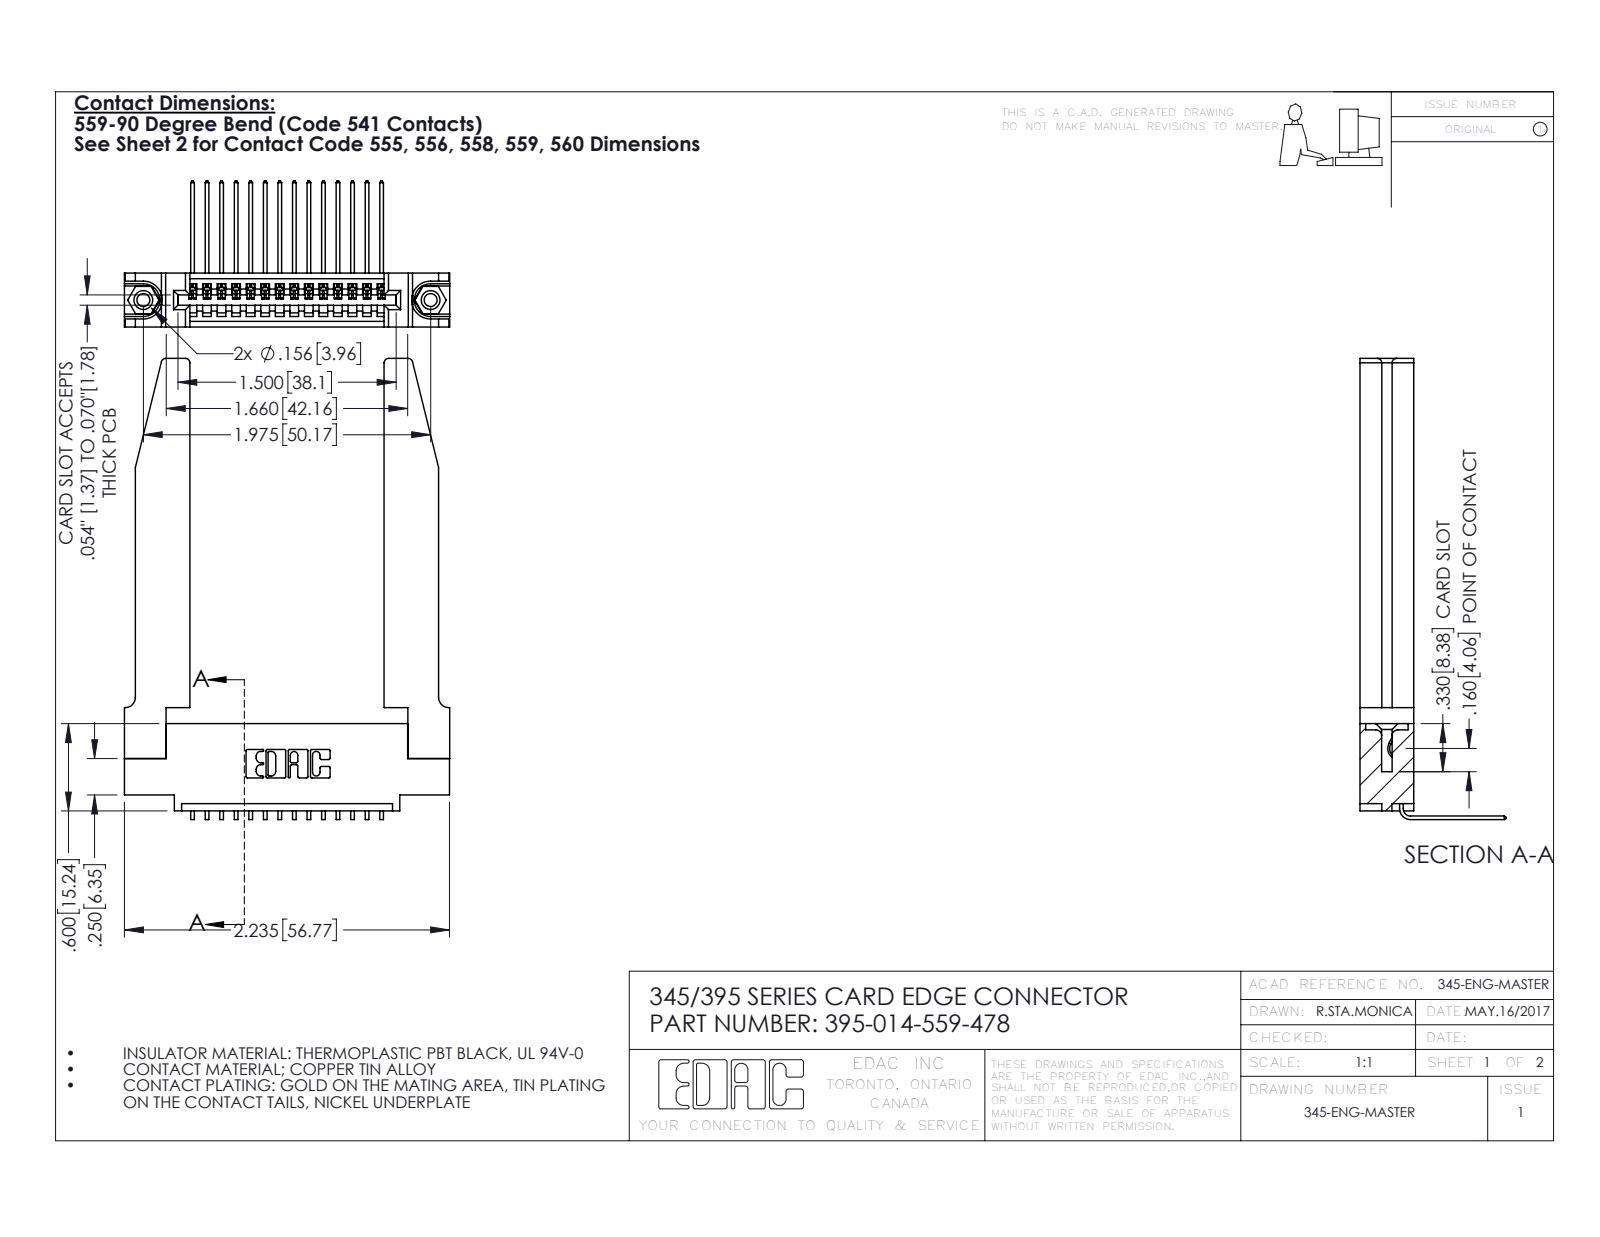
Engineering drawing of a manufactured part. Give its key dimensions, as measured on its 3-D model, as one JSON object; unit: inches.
{"part_name": "345-292-001_558 559 Tail - 1; 345-250-001_345-250-001-102; 345-220-078_345-220-078; 395-014-559-478 (+1 more)", "step_written_by": "SolidWorks 2016 (CONFIG_CONTROL_DESIGN)", "units": "inches", "bodies": {"solids": 19, "faces": 1204, "planar": 814, "cylindrical": 338, "other": 52}, "overall_size": [3.169, 2.236, 1.005], "volume_in3": 0.788, "surface_area_in2": 21.16, "round_holes": [[0.089, 2], [0.125, 2], [0.156, 2], [0.064, 1]], "round_bosses_or_shafts": [[0.155, 2]], "partial_cylinders_radius": [[0.006, 28], [0.01, 22], [0.03, 8], [0.007, 6], [0.031, 6], [0.026, 3], [0.031, 2], [0.04, 2]], "face_to_face_distances": [0.37, 0.072, 0.298, 0.148, 0.15, 0.22, 0.077, 1.335, 0.2, 0.098], "hole_center_spacings": [0.27, 1.742, 1.975]}
